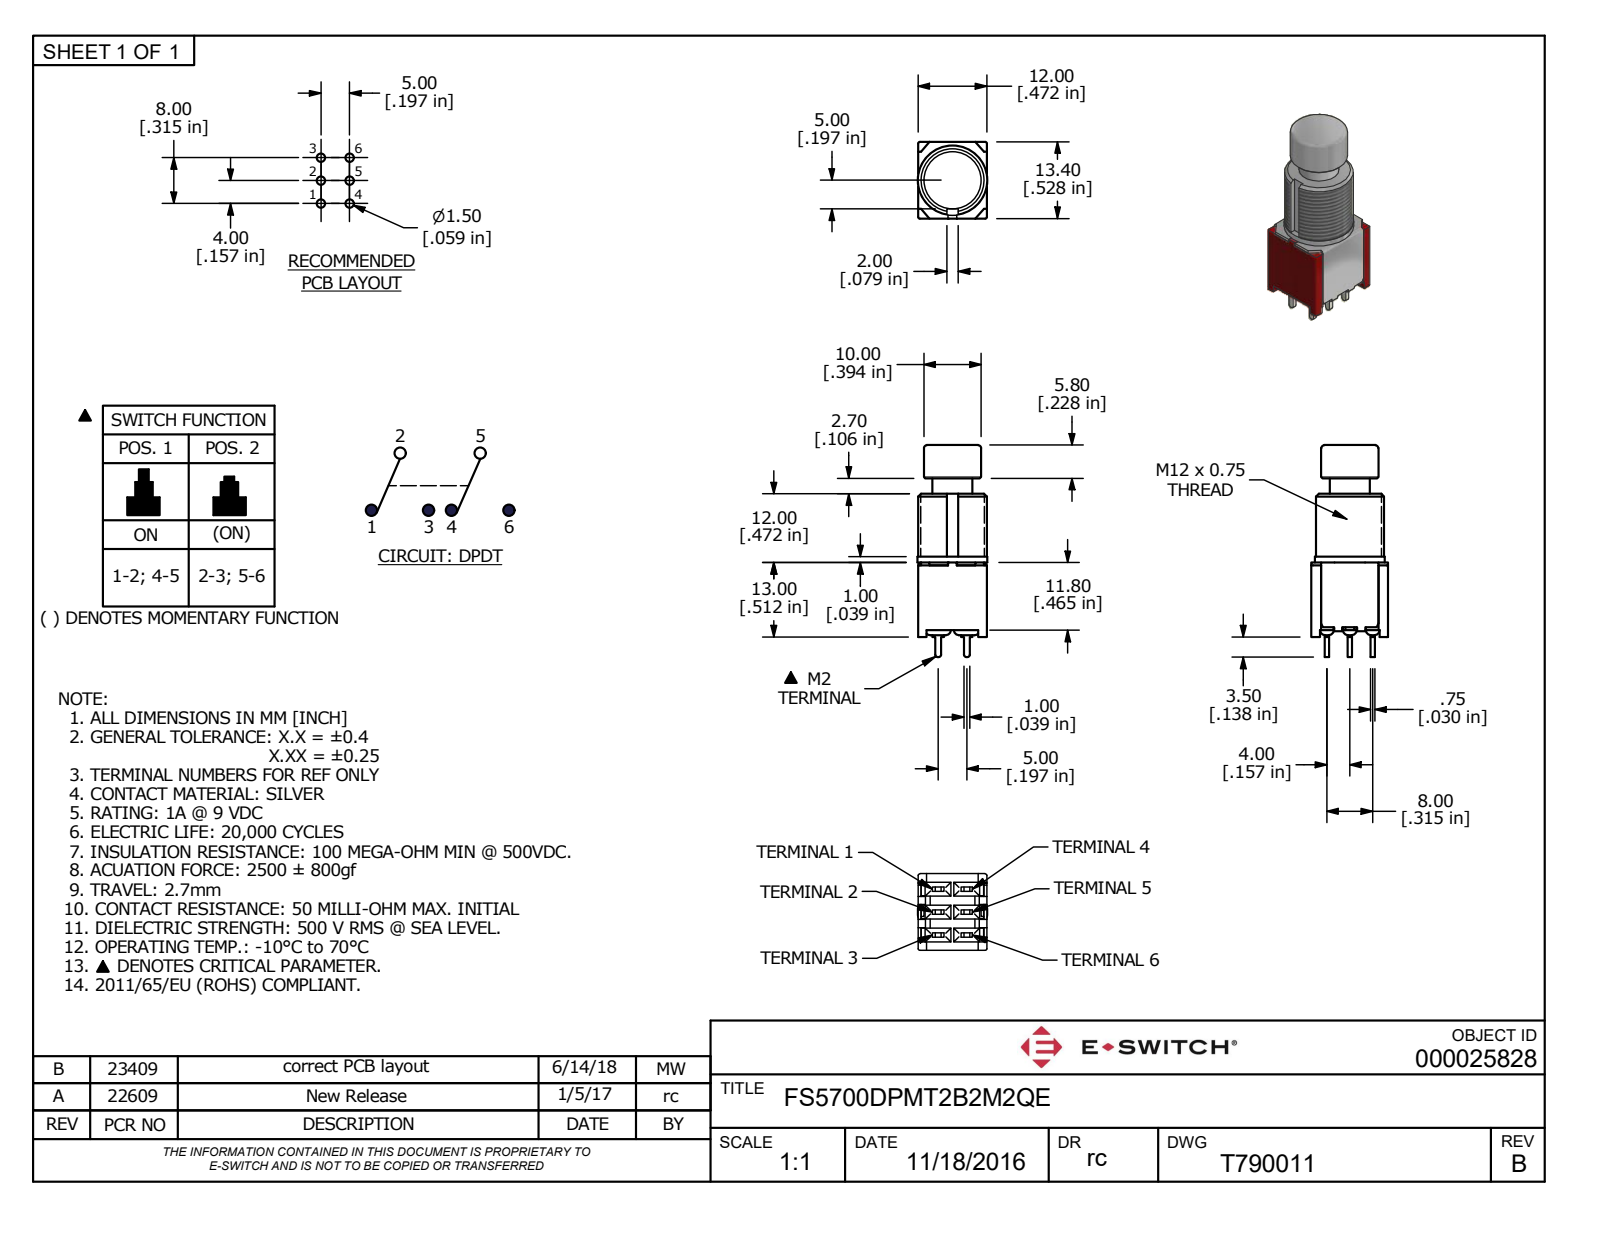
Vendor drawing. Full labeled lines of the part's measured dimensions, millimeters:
Part name (STEP PRODUCT): FS5700DPMT2B2M2QE
STEP written by: Autodesk Inventor 2022 (AUTOMOTIVE_DESIGN)
Units: millimetres
Bodies: 1 solid, 338 faces (252 planar, 83 cylindrical, 3 other)
Overall size (bounding box): 37 × 13.4 × 12.2
Volume: 2 131 mm³ · Surface area: 3 332 mm²
Round holes (diameter × count): ⌀9 ×1
Round bosses / shafts (diameter × count): ⌀12.2 ×1, ⌀12 ×1, ⌀10 ×1, ⌀7 ×1
Partial cylindrical surfaces — rounded edges, fillets, slot ends (radius × count): R0.2 ×26, R0.9 ×10, R0.3 ×4, R0.4 ×4, R0.5 ×4, R0.1 ×2
Main face-to-face distances: 1.2, 0.5, 11, 10.8, 0.7, 10.3, 11.5, 12, 0.55, 11.45
